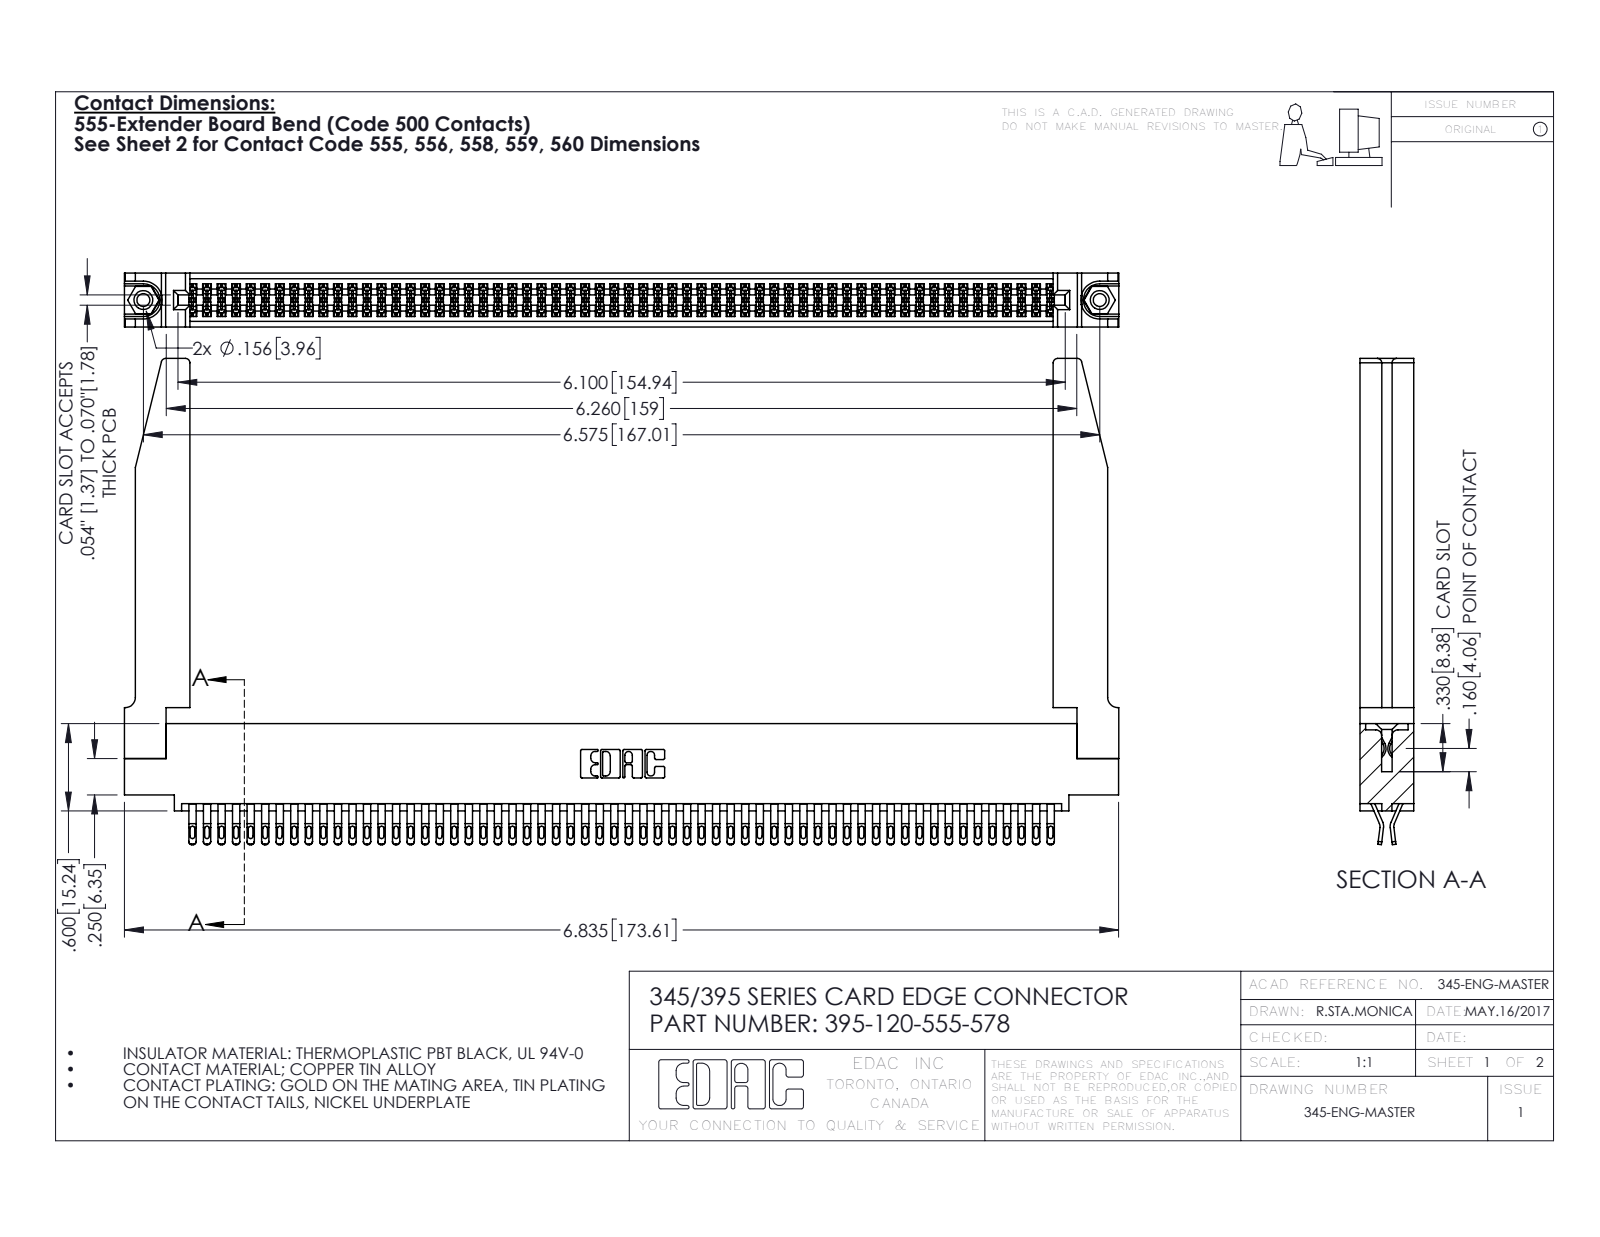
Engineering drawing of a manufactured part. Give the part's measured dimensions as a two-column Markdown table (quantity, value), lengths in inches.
| quantity | value |
| --- | --- |
| part name | 345-292-001_555 Tail; 345-250-001_345-250-001-102; 395-120-555-578; 345-220-078_345-220-078 (+1 more) |
| STEP written by | SolidWorks 2016 (CONFIG_CONTROL_DESIGN) |
| units | inches |
| bodies | 125 solids, 7084 faces (3946 planar, 3086 cylindrical, 52 other) |
| overall size | 6.836 × 3.342 × 0.37 |
| volume | 1.53 in³ |
| surface area | 52.82 in² |
| round holes (diameter × count) | 0.089 × 2, 0.125 × 2, 0.156 × 2, 0.064 × 1 |
| round bosses / shafts (diameter × count) | 0.155 × 2 |
| partial cylindrical surfaces (radius × count) | 0.016 × 300, 0.02 × 240, 0.006 × 180, 0.01 × 22, 0.03 × 8, 0.007 × 6, 0.031 × 6, 0.026 × 3 |
| main face-to-face distances | 0.072, 0.298, 0.37, 0.025, 0.098, 0.272, 0.2, 0.225, 0.175, 0.148 |
| hole center spacings | 0.27, 6.339, 6.575 |
